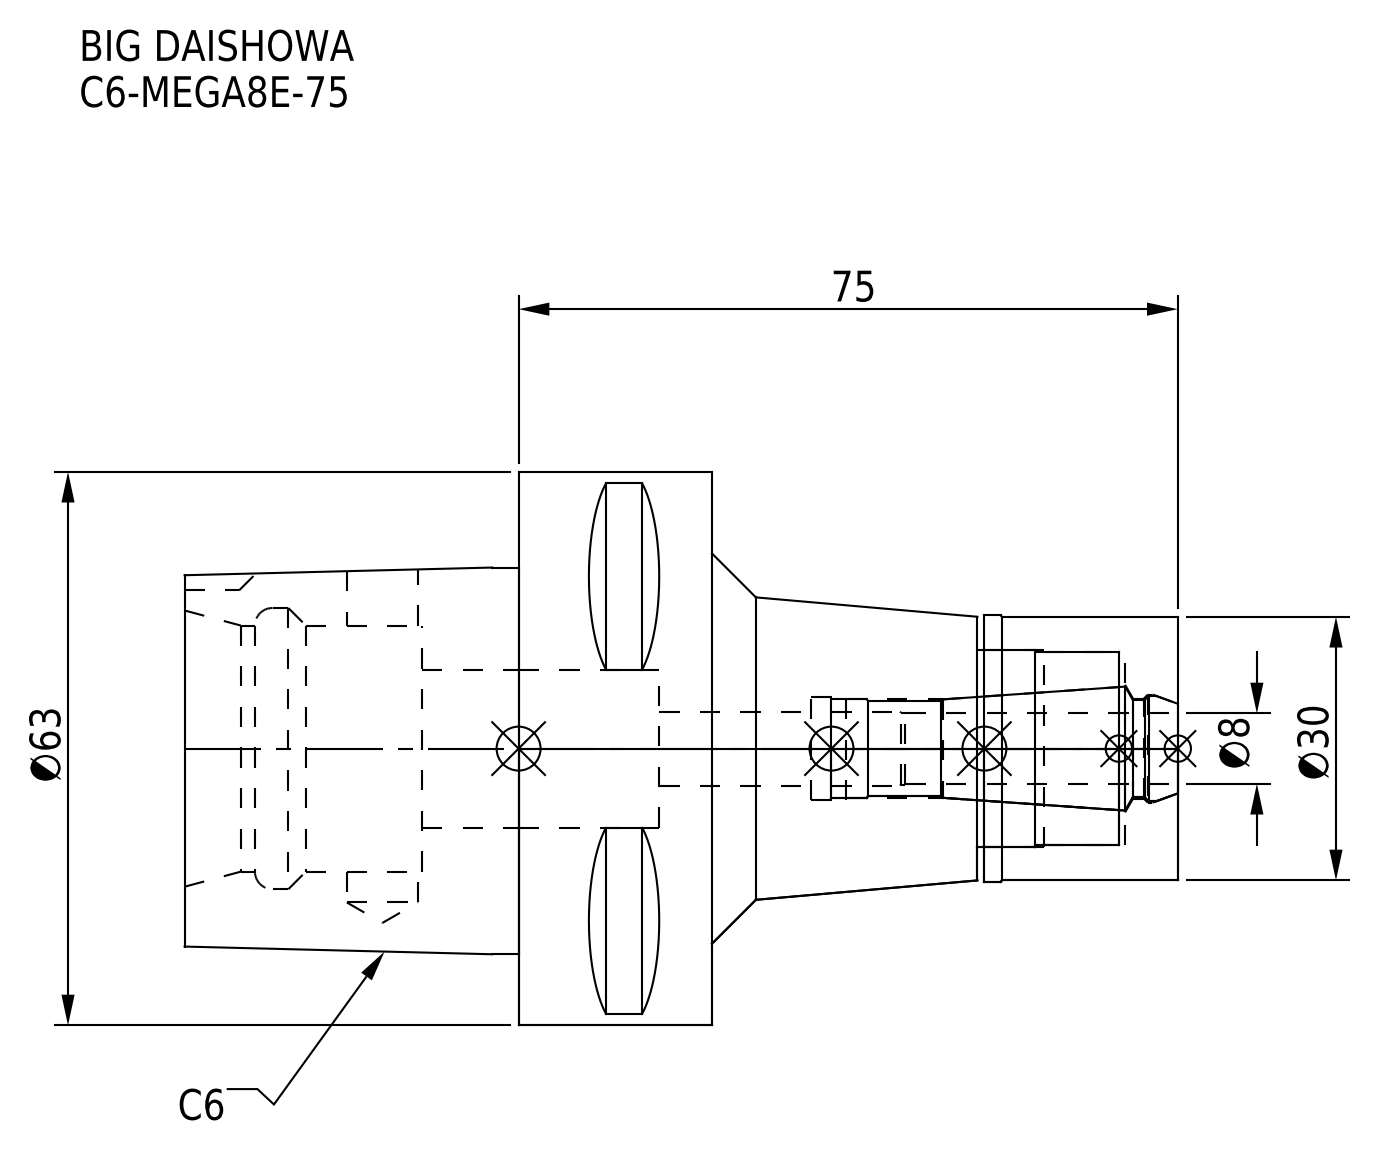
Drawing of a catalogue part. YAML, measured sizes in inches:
part_name: "C6-MEGA8E-75_1.stp; MEN8_1.stp; DXF_TEMP_ASSY_ASM_4_ASM.stp; C6-MEGA8E-75-080.stp (+3 more)"
step_written_by: "SolidWorks 2019 (CONFIG_CONTROL_DESIGN)"
units: inches
bodies: {solids: 2, faces: 97, planar: 36, cylindrical: 37, other: 24}
overall_size: [4.449, 2.48, 2.48]
volume: 8.131
surface_area: 46.73
round_holes:
  - {diameter: 0.319, count: 1}
  - {diameter: 0.331, count: 1}
  - {diameter: 0.441, count: 1}
  - {diameter: 0.449, count: 1}
  - {diameter: 0.465, count: 1}
  - {diameter: 0.484, count: 1}
  - {diameter: 0.709, count: 1}
  - {diameter: 0.866, count: 1}
  - {diameter: 0.886, count: 1}
  - {diameter: 1.102, count: 1}
  - {diameter: 1.26, count: 1}
round_bosses_or_shafts:
  - {diameter: 2.48, count: 1}
  - {diameter: 1.193, count: 1}
  - {diameter: 1.181, count: 1}
partial_cylinders:
  - {radius: 0.197, count: 1}
face_to_face_distances: [0.866, 2.087, 2.953, 1.063, 4.449, 2.362, 1.496, 0.236, 0.63, 3.386]
